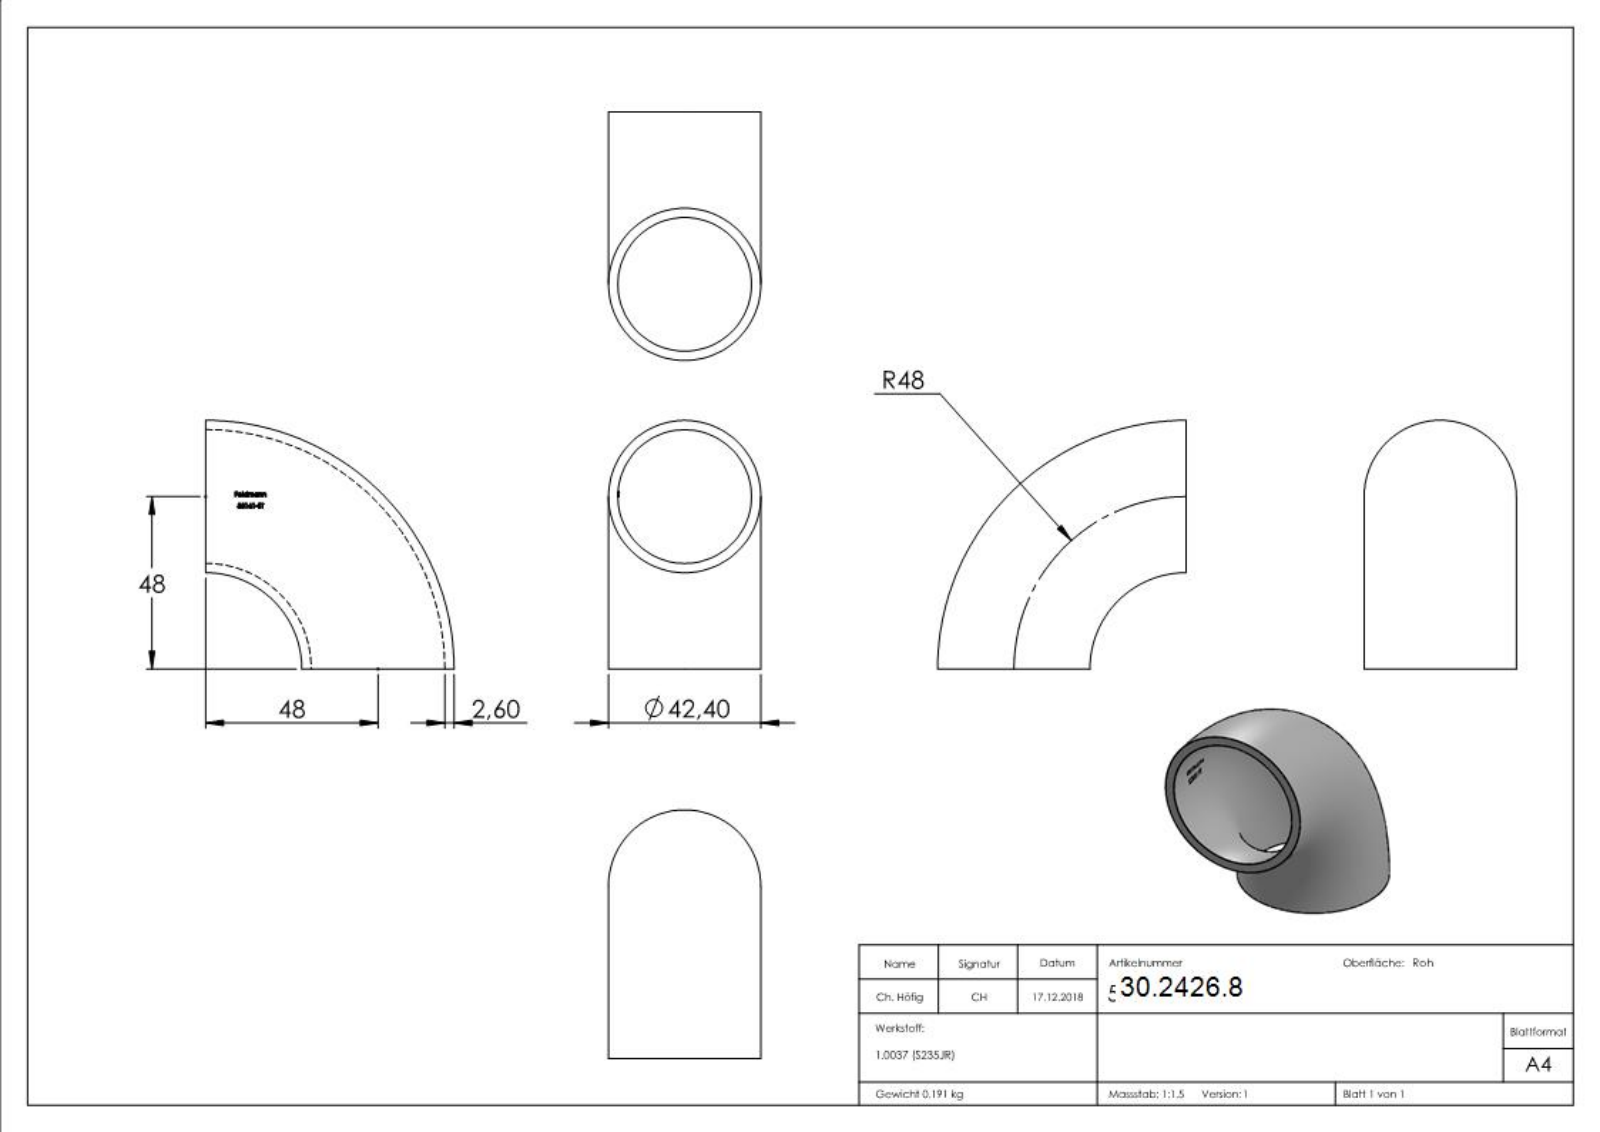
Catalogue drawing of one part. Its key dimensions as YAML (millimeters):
part_name: "55161-ST"
step_written_by: "SolidWorks 2015 (CONFIG_CONTROL_DESIGN)"
units: millimeters
bodies: {solids: 1, faces: 209, planar: 97, cylindrical: 0, other: 112}
overall_size: [69.2, 69.2, 42.4]
volume: 24511
surface_area: 19513
face_to_face_distances: [3.09, 2.97, 3.27, 3.54, 2.02, 0.39, 2.04, 3.66, 2.39, 4.43]
